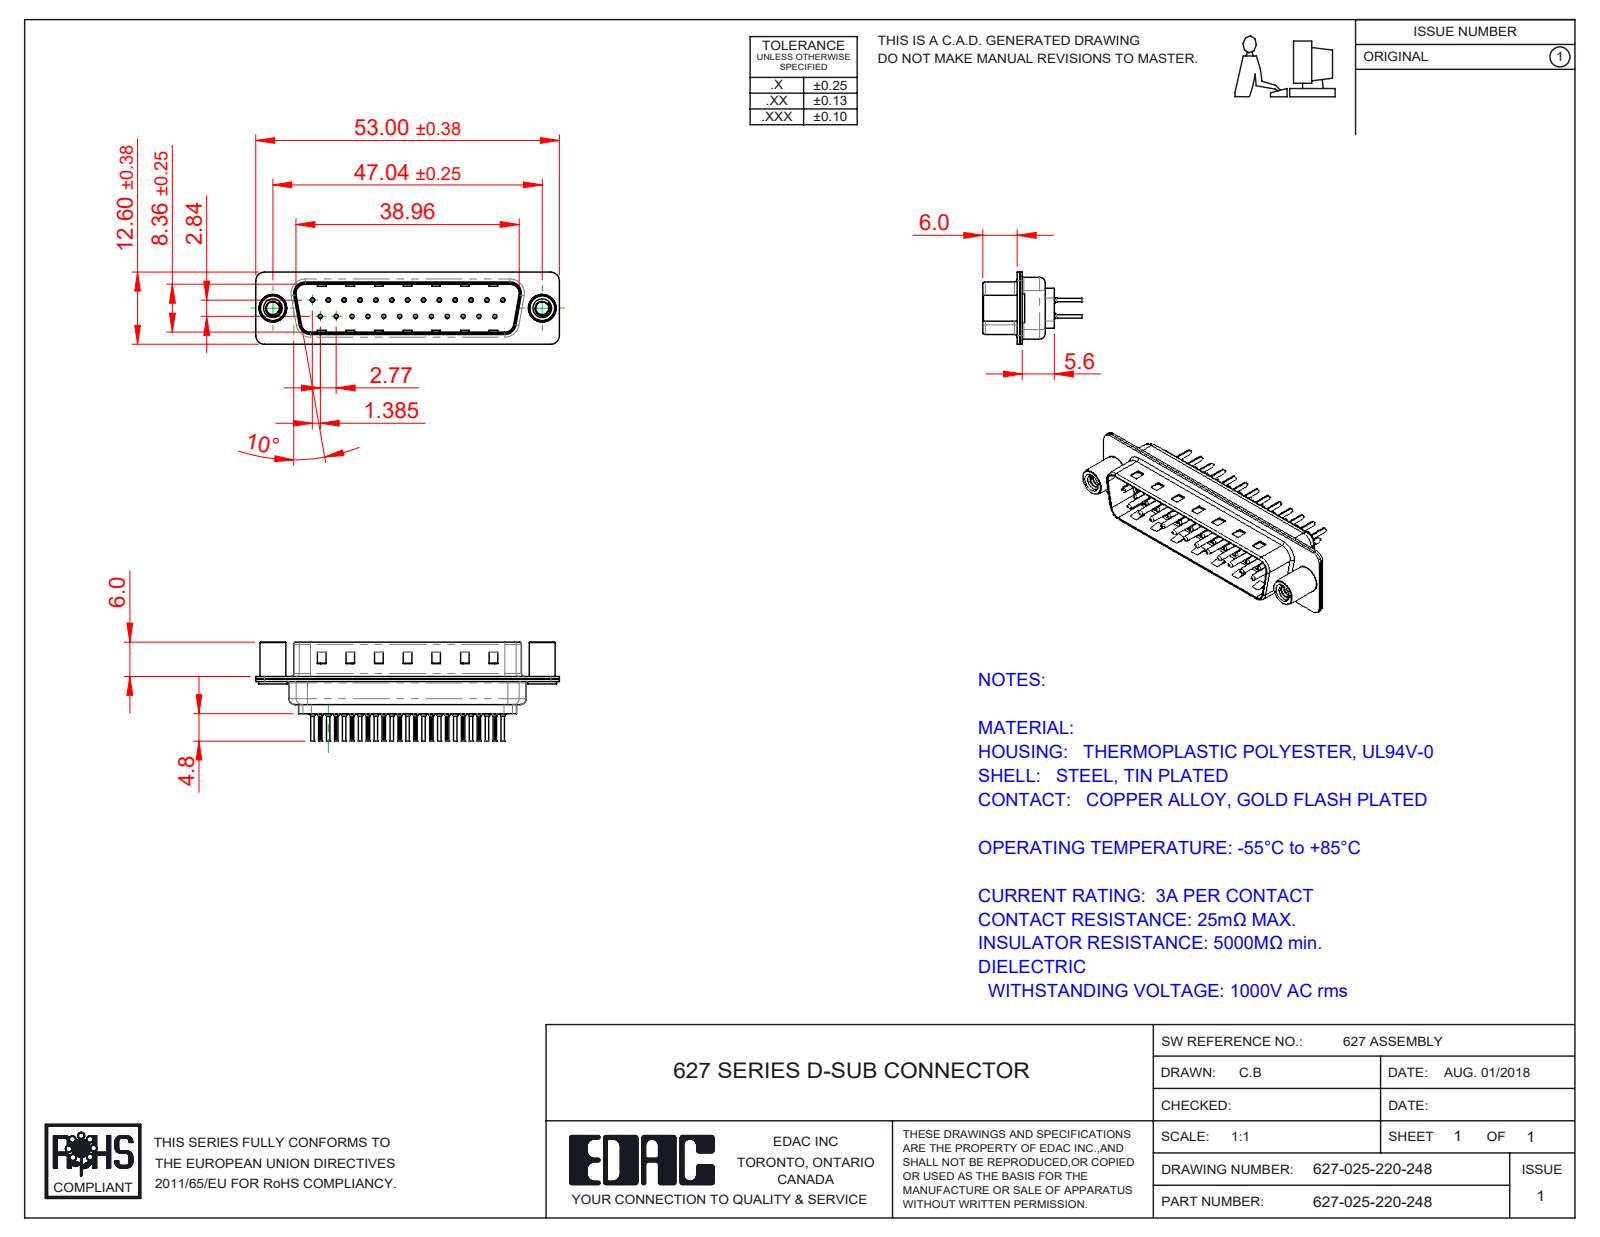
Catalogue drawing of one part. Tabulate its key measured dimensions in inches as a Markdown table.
| quantity | value |
| --- | --- |
| part name | 627 Contact Row 2_20L; 627 4-40 Threaded Standoff; 627 Shell Front_25 Contacts; 627 Housing_25 LP (+3 more) |
| STEP written by | SolidWorks 2020 (CONFIG_CONTROL_DESIGN) |
| units | inches |
| bodies | 30 solids, 2860 faces (773 planar, 1090 cylindrical, 997 other) |
| overall size | 2.087 × 0.681 × 0.496 |
| volume | 0.168 in³ |
| surface area | 12.4 in² |
| round holes (diameter × count) | 0.008 × 25, 0.014 × 25, 0.043 × 25, 0.063 × 25, 0.089 × 2, 0.157 × 2, 0.189 × 2 |
| round bosses / shafts (diameter × count) | 0.079 × 25, 0.059 × 25, 0.03 × 25, 0.024 × 25, 0.197 × 2, 0.193 × 2, 0.177 × 2 |
| partial cylindrical surfaces (radius × count) | 0.004 × 50, 0.059 × 16, 0.079 × 12, 0.02 × 8, 0.063 × 8, 0.01 × 4, 0.024 × 4, 0.026 × 4 |
| main face-to-face distances | 0.016, 0.018, 0.032, 0.377, 0.035, 0.345, 0.059, 0.055, 0.256, 0.238 |
| hole center spacings | 0.124, 0.327, 0.109, 0.218, 0.436, 0.654, 0.198, 0.198 |
